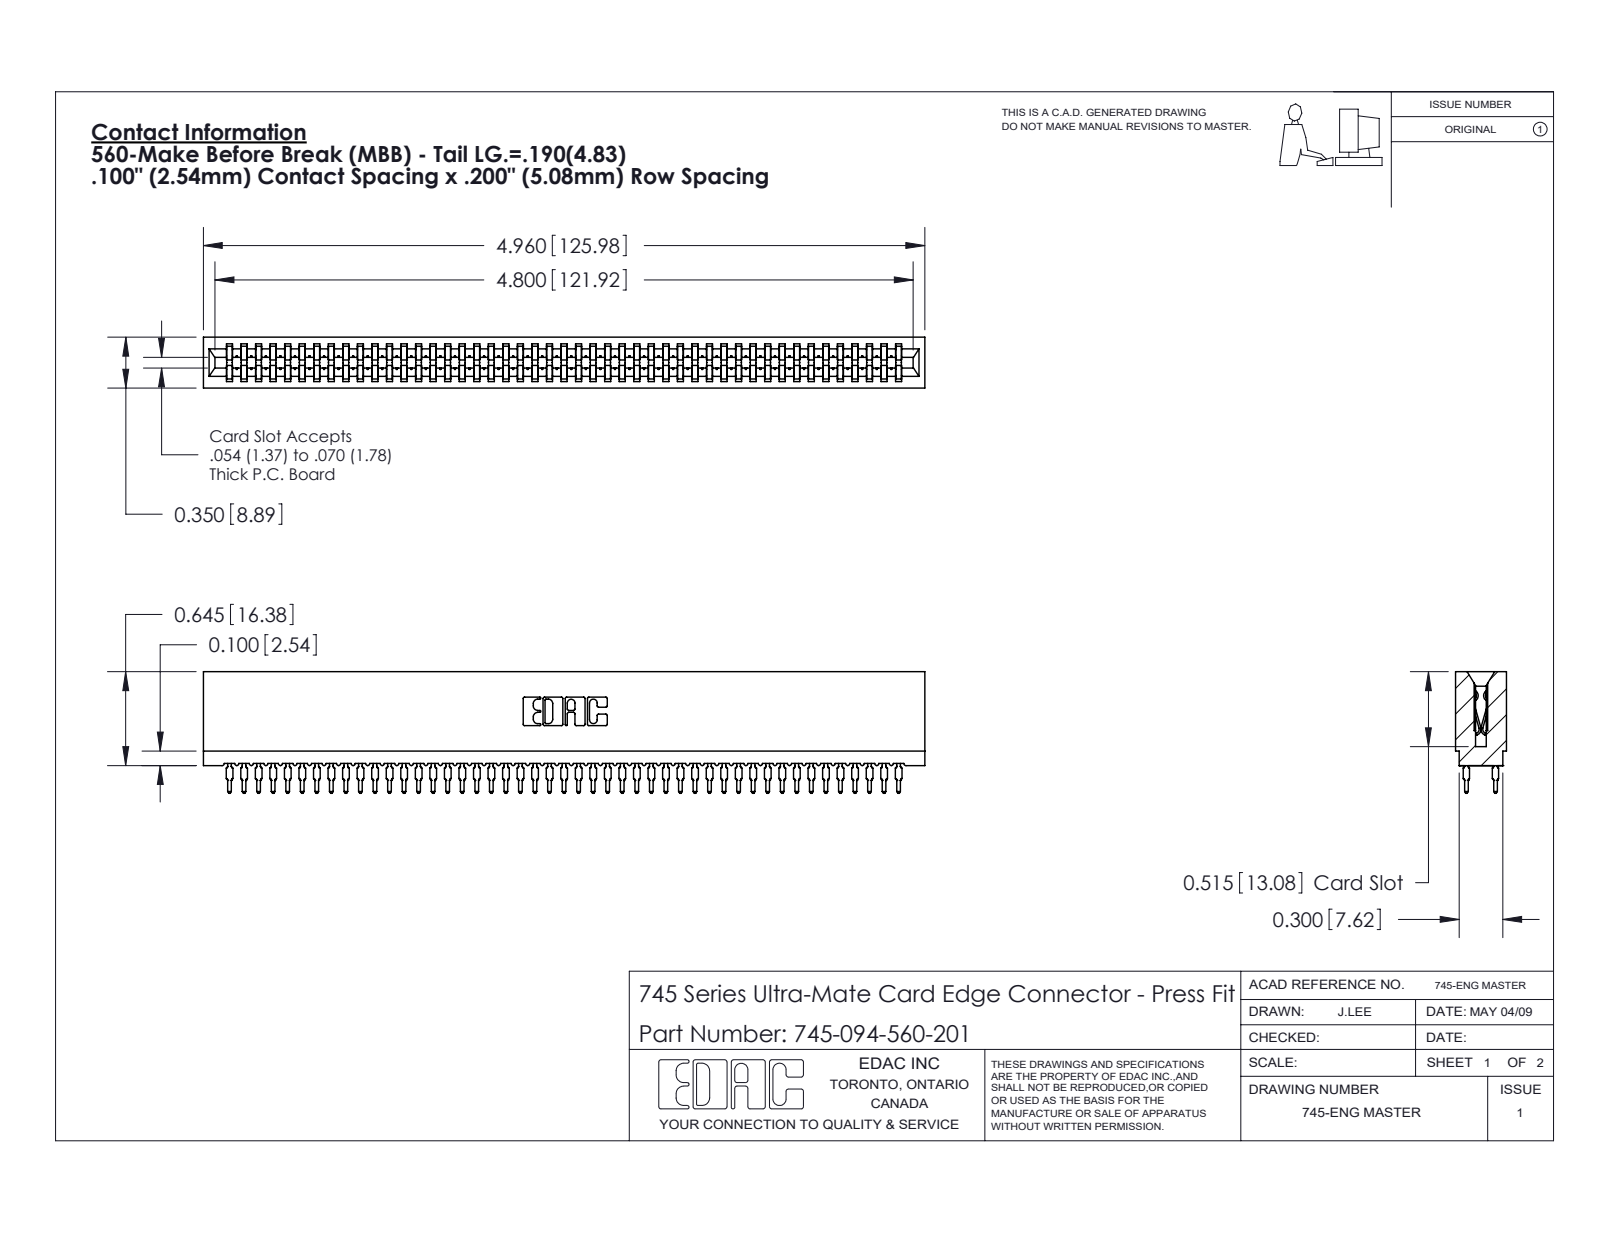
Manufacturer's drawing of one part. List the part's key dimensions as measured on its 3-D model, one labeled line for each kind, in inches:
Part name (STEP PRODUCT): 745-094-560-201; 745 Part_Insulator Option - 01; 745-292-001_560
STEP written by: SolidWorks 2020 (CONFIG_CONTROL_DESIGN)
Units: inches
Bodies: 95 solids, 9354 faces (4849 planar, 2061 cylindrical, 2444 other)
Overall size (bounding box): 4.96 × 0.836 × 0.35
Volume: 0.712 in³ · Surface area: 39.23 in²
Partial cylindrical surfaces — rounded edges, fillets, slot ends (radius × count): R0.021 ×188, R0.015 ×94, R0.01 ×22, R0.005 ×8, R0.011 ×8, R0.007 ×6, R0.031 ×6, R0.026 ×3
Main face-to-face distances: 0.35, 0.063, 0.287, 0.2, 0.045, 0.305, 0.018, 0.243, 0.138, 0.212
